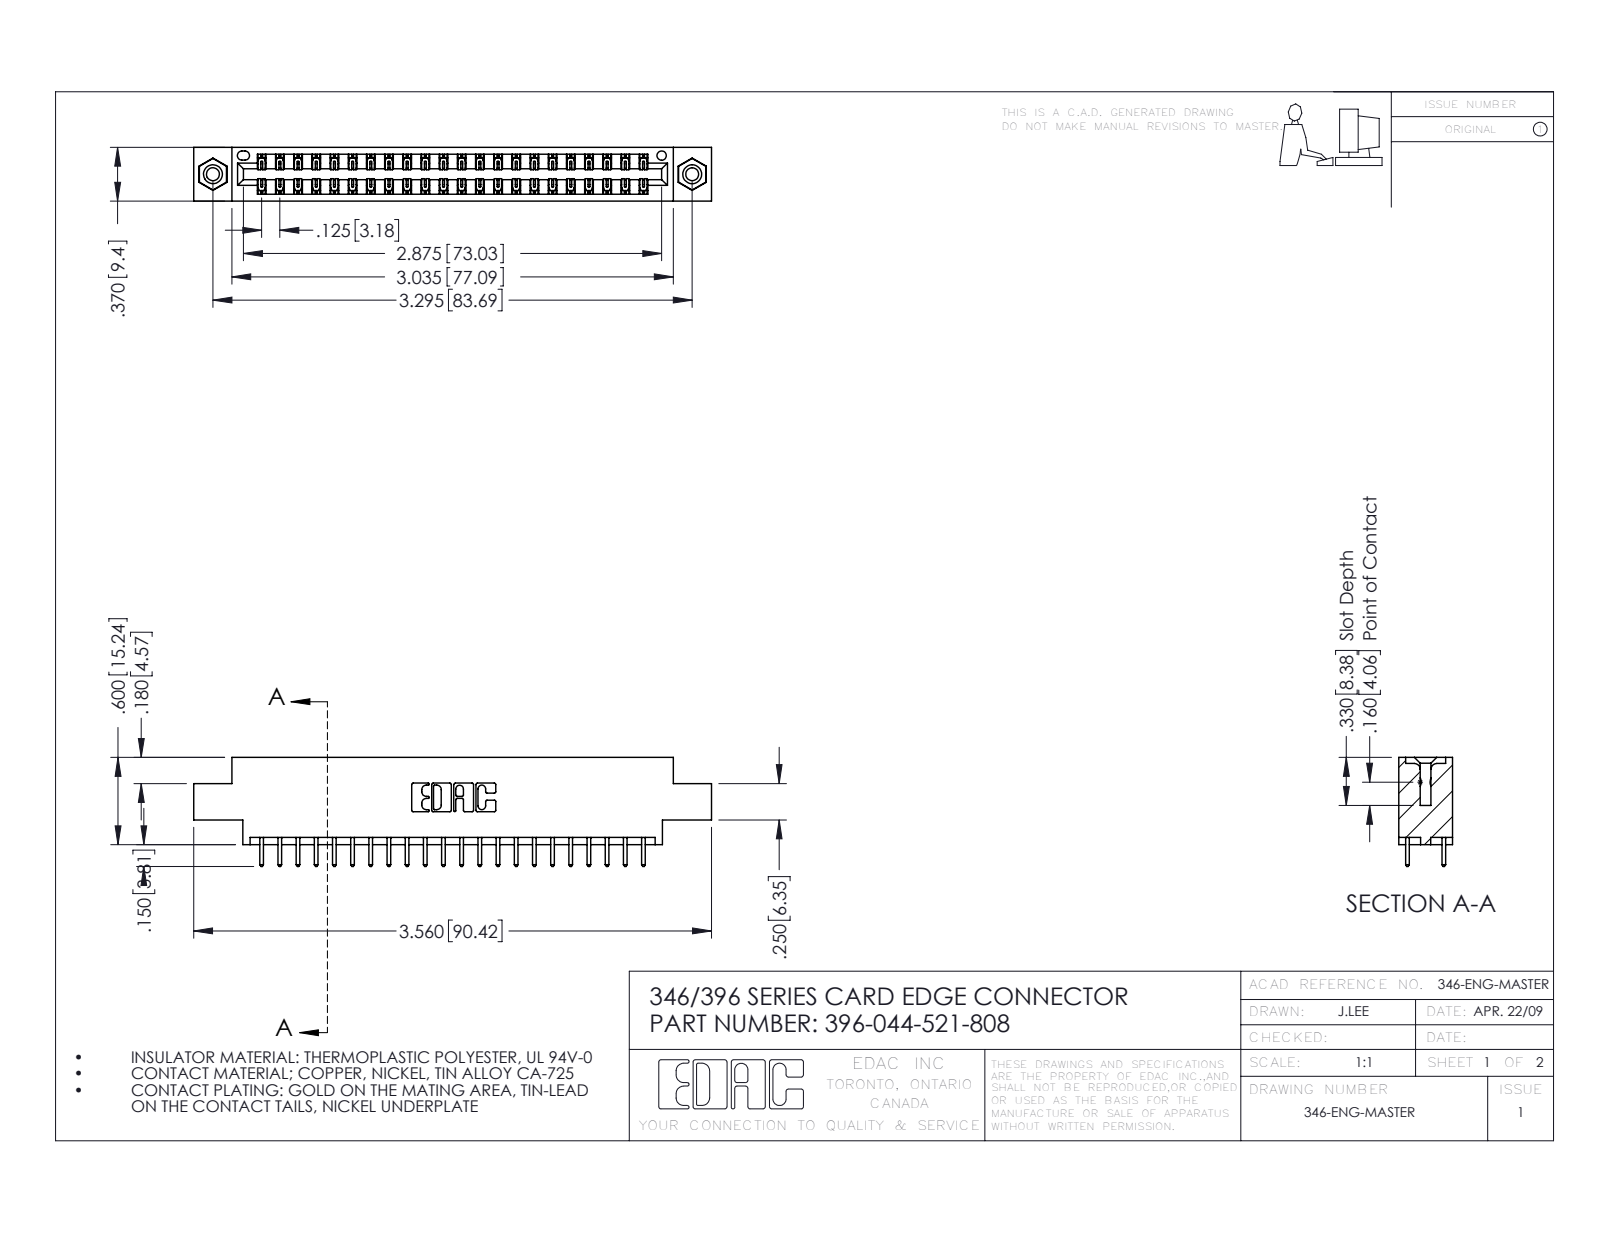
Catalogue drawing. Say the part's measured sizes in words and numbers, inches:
The part is named "346 Part_0.170 Offset - 0.156 Dia-TI; 345-292-001_345-293-121; 396-044-521-808; 345-250-001_345-250-003-102". Its 3-D file was written by "SolidWorks 2016 (CONFIG_CONTROL_DESIGN)". It is 47 solids with 2474 faces: 1652 planar, 806 cylindrical and 16 other. Overall it measures 3.56 by 0.75 by 0.37 inches. Its volume is 0.518 cubic inches and its surface area 17.71 square inches. Round holes: 2 of diameter 0.089, 2 of diameter 0.125, 2 of diameter 0.156, 1 of diameter 0.064. Round bosses or shafts: 2 of diameter 0.155. Partial cylindrical surfaces (rounded edges, fillets, slot ends): 66 of radius 0.006, 44 of radius 0.01, 22 of radius 0.01, 6 of radius 0.007, 6 of radius 0.031, 3 of radius 0.026, 2 of radius 0.014, 2 of radius 0.022. The main face-to-face distances are 0.048, 0.322, 0.37, 0.25, 0.072, 0.298, 0.025, 0.275, 0.222, 0.148. The hole center spacings are 0.246, 3.087, 3.295.
